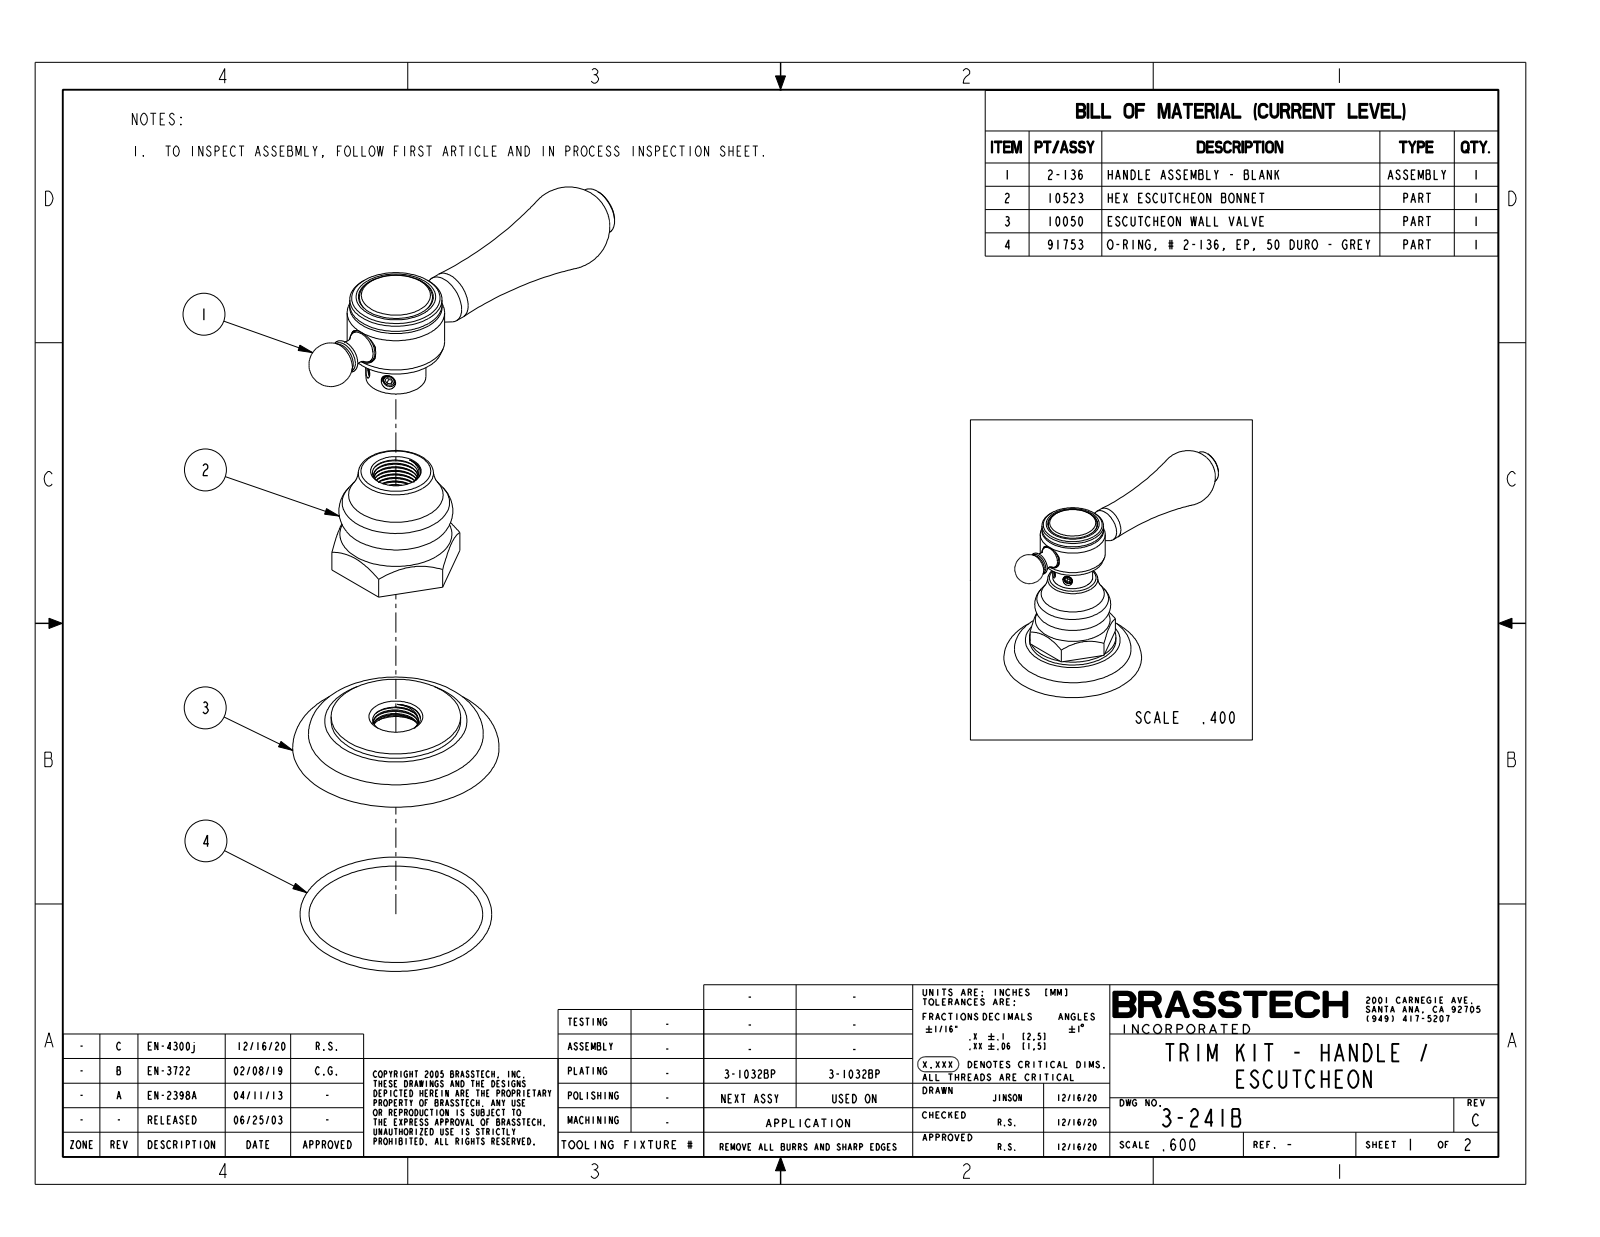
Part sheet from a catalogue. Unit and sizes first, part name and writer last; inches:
Units: inches
Overall size (bounding box): 4.675 × 2.898 × 2.36
Round holes (diameter × count): ⌀0.41 ×1
Round bosses / shafts (diameter × count): ⌀1.482 ×1, ⌀1.115 ×1, ⌀1.055 ×1, ⌀0.687 ×1, ⌀0.563 ×1, ⌀0.4 ×1, ⌀0.394 ×1, ⌀0.392 ×1
Main face-to-face distances: 1.313, 1.687, 0.375, 1.312, 1.703, 1.328, 0.016, 1.313, 0.437, 0.062
Volume: 4.794 in³ · Surface area: 26.55 in²
Bodies: 1 solid, 109 faces (33 planar, 22 cylindrical, 54 other)
Part name (STEP PRODUCT): 3-241B
STEP written by: CREO PARAMETRIC BY PTC INC, 2018400 (CONFIG_CONTROL_DESIGN)
